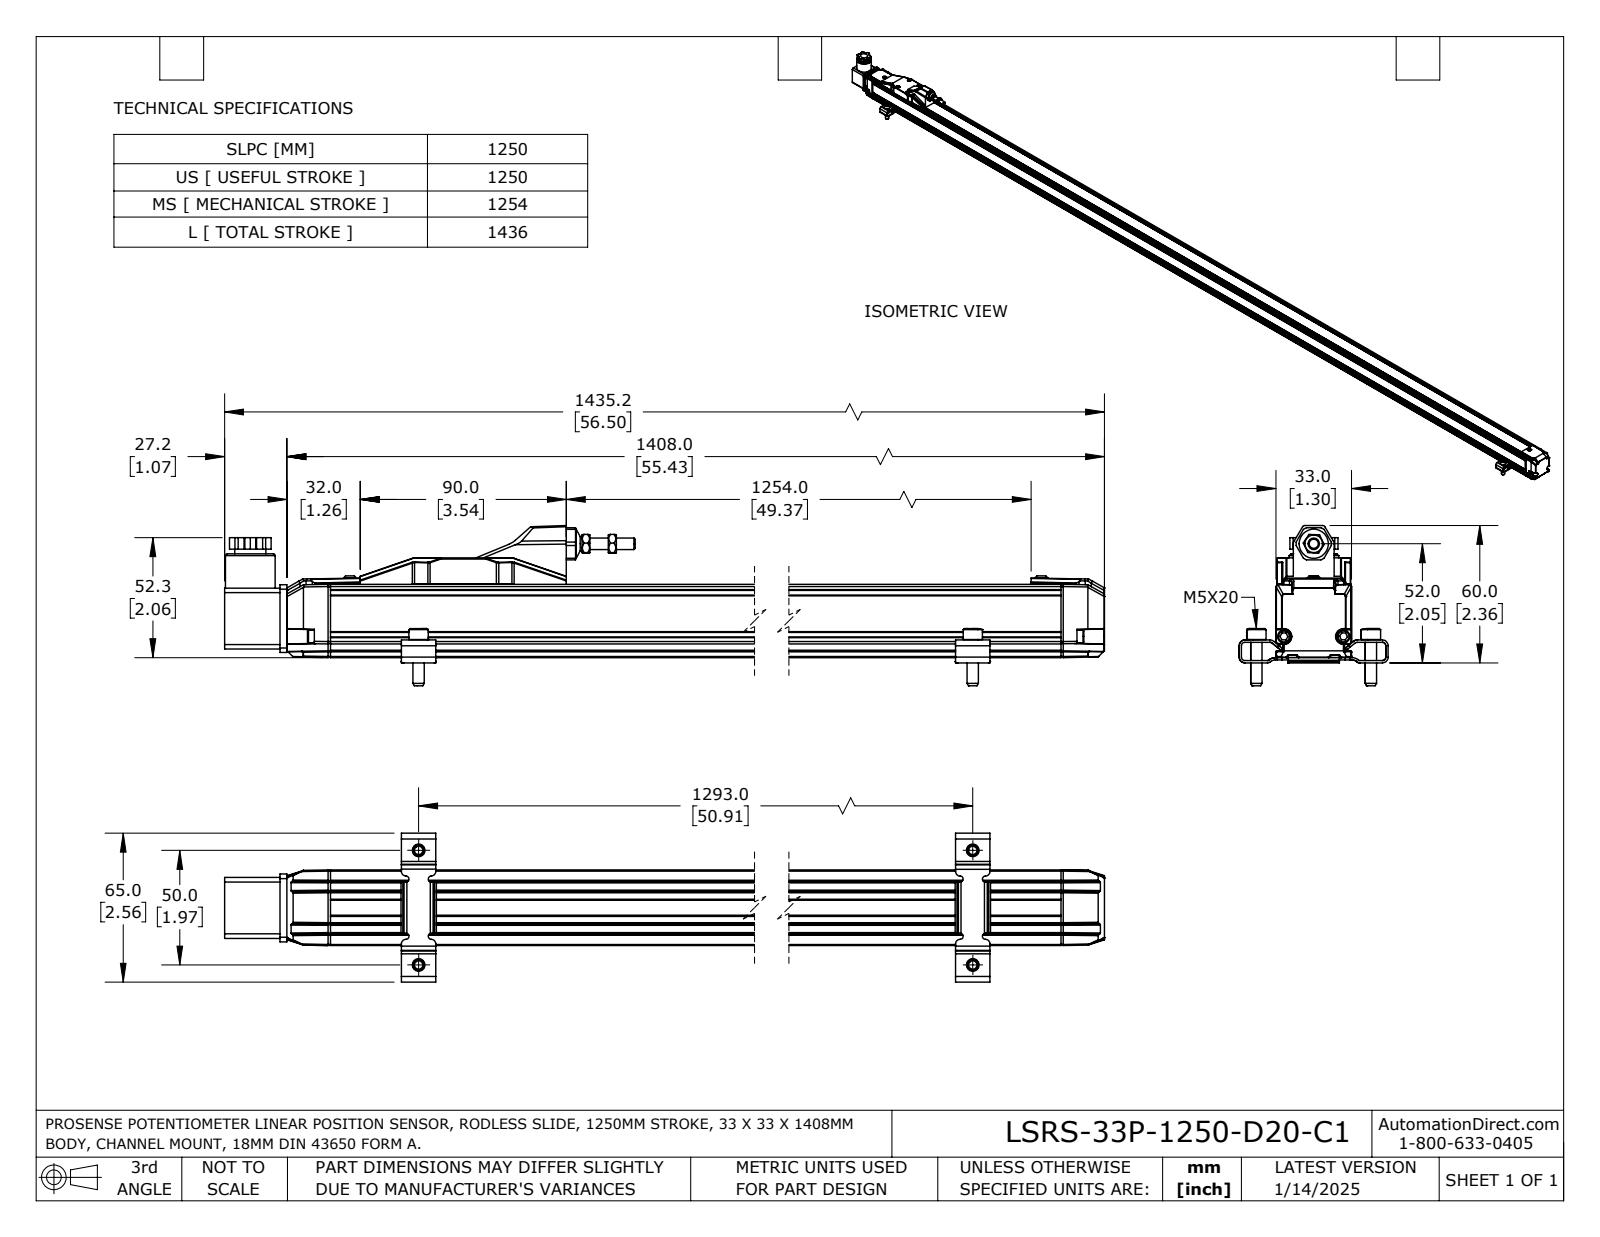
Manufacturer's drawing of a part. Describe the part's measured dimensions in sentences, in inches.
The part is named "LSRS-33P-1250-D20-C1". Its 3-D file was written by "SolidWorks 2023 (AUTOMOTIVE_DESIGN)". It is 10 solids with 1310 faces: 821 planar, 357 cylindrical and 132 other. Overall it measures 56.504 by 2.754 by 2.559 inches. Its volume is 82.8 cubic inches and its surface area 463.6 square inches. Round holes: 4 of diameter 0.185, 4 of diameter 0.217, 2 of diameter 0.106, 2 of diameter 0.13, 1 of diameter 0.157, 1 of diameter 0.197, 1 of diameter 0.209, 1 of diameter 0.232, 1 of diameter 0.236, 1 of diameter 0.276, 1 of diameter 0.394, 1 of diameter 0.413. Round bosses or shafts: 4 of diameter 0.331, 4 of diameter 0.193, 4 of diameter 0.181, 4 of diameter 0.113, 2 of diameter 0.22, 2 of diameter 0.217, 2 of diameter 0.118, 2 of diameter 0.098. Partial cylindrical surfaces (rounded edges, fillets, slot ends): 78 of radius 0.02, 62 of radius 0.008, 44 of radius 0.079, 26 of radius 0.118, 10 of radius 0.039, 8 of radius 0.051, 8 of radius 0.059, 8 of radius 0.157. The main face-to-face distances are 1.299, 0.118, 1.244, 1.167, 0.237, 1.007, 0.035, 0.014, 1.285, 0.443. The hole center spacings are 0.597, 0.787, 0.933, 1.221, 1.286, 1.673, 1.969, 49.747.
